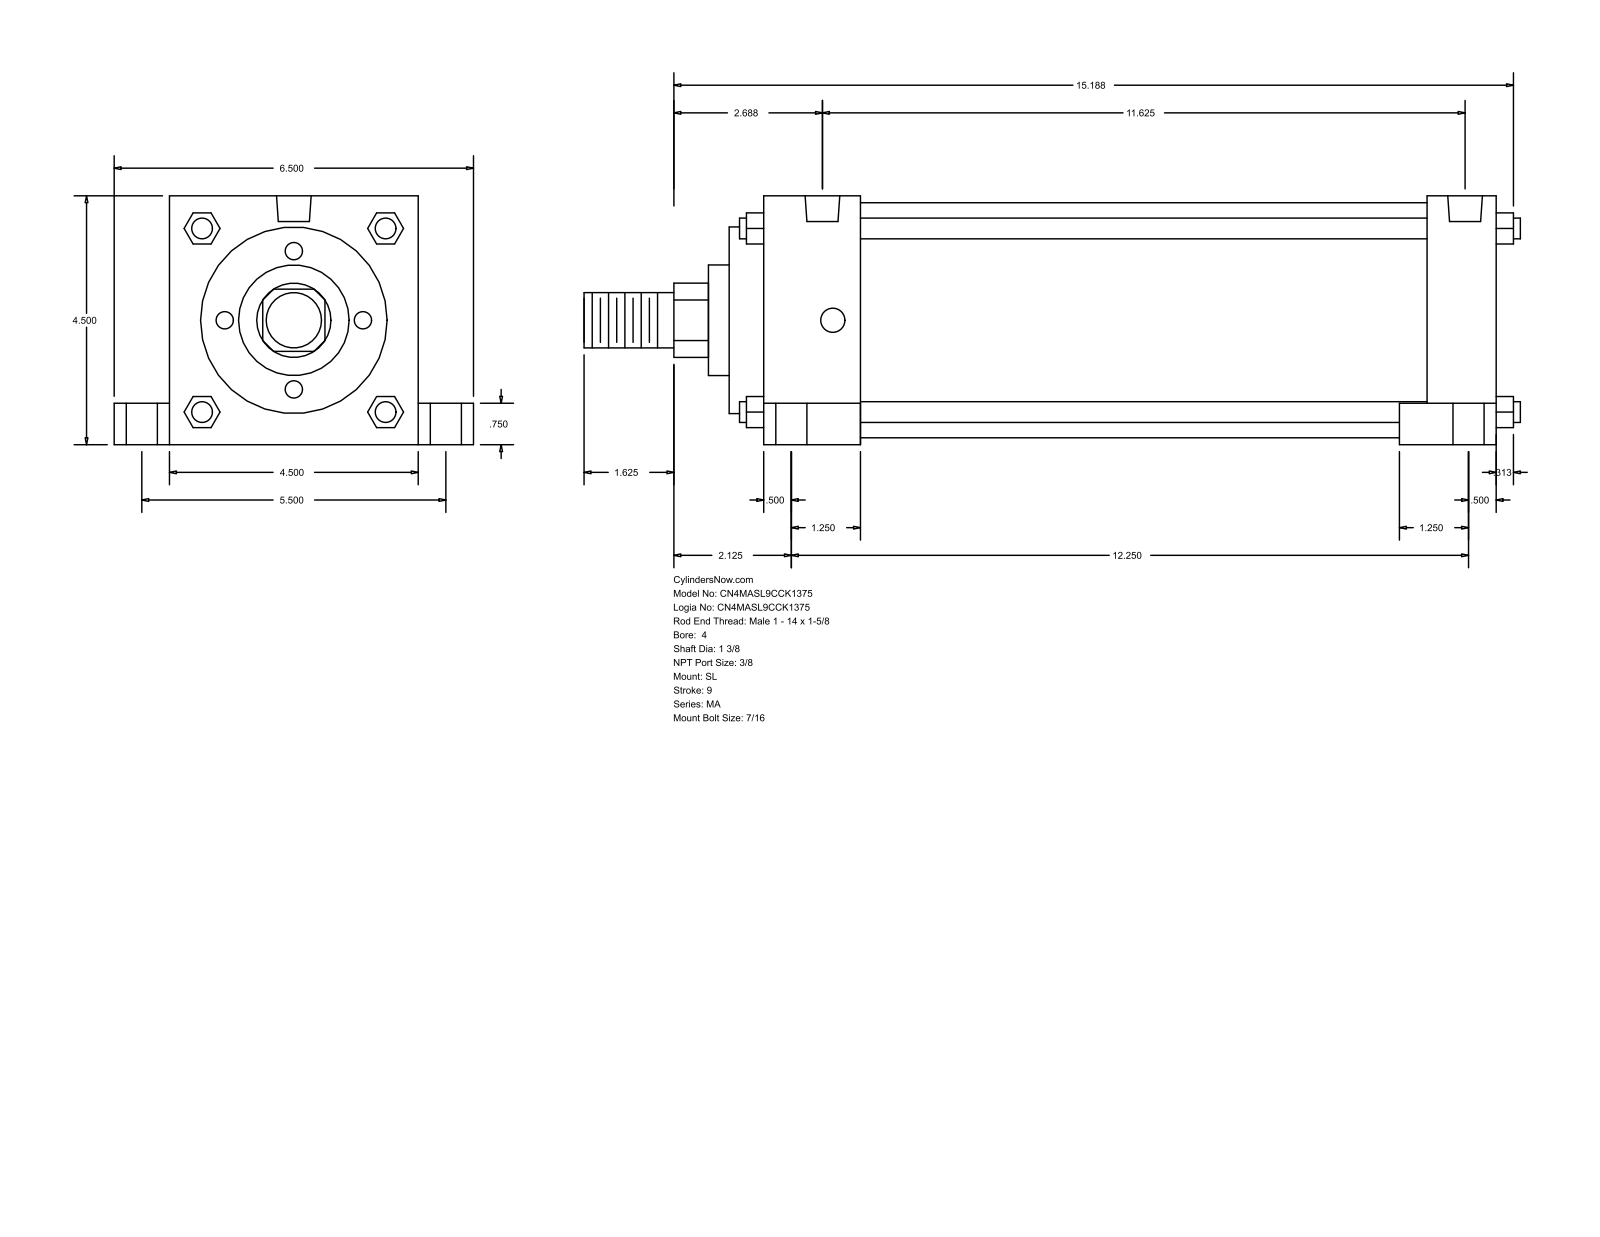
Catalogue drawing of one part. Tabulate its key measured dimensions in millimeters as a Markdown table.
| quantity | value |
| --- | --- |
| part name | MA_SL__0400_1.375 |
| STEP written by | GSSL Pune (CONFIG_CONTROL_DESIGN) |
| units | millimeters |
| bodies | 0 solids, 150 faces (113 planar, 37 cylindrical, 0 other) |
| overall size | 430.21 × 165.1 × 114.3 |
| round holes (diameter × count) | 11.11 × 4, 14.29 × 4, 20.64 × 4, 15.93 × 2 |
| round bosses / shafts (diameter × count) | 9.53 × 4, 107.95 × 1, 85.72 × 1, 50.8 × 1, 34.92 × 1, 25.4 × 1 |
| partial cylindrical surfaces (radius × count) | 17.06 × 1 |
| main face-to-face distances | 114.3, 336.55, 260.35, 352.42, 15.87, 60.32, 44.45, 292.1, 320.67, 304.8 |
| hole center spacings | 4.77, 69.87, 70.14, 71.29, 72.4, 139.7, 285.74, 290.51 |
